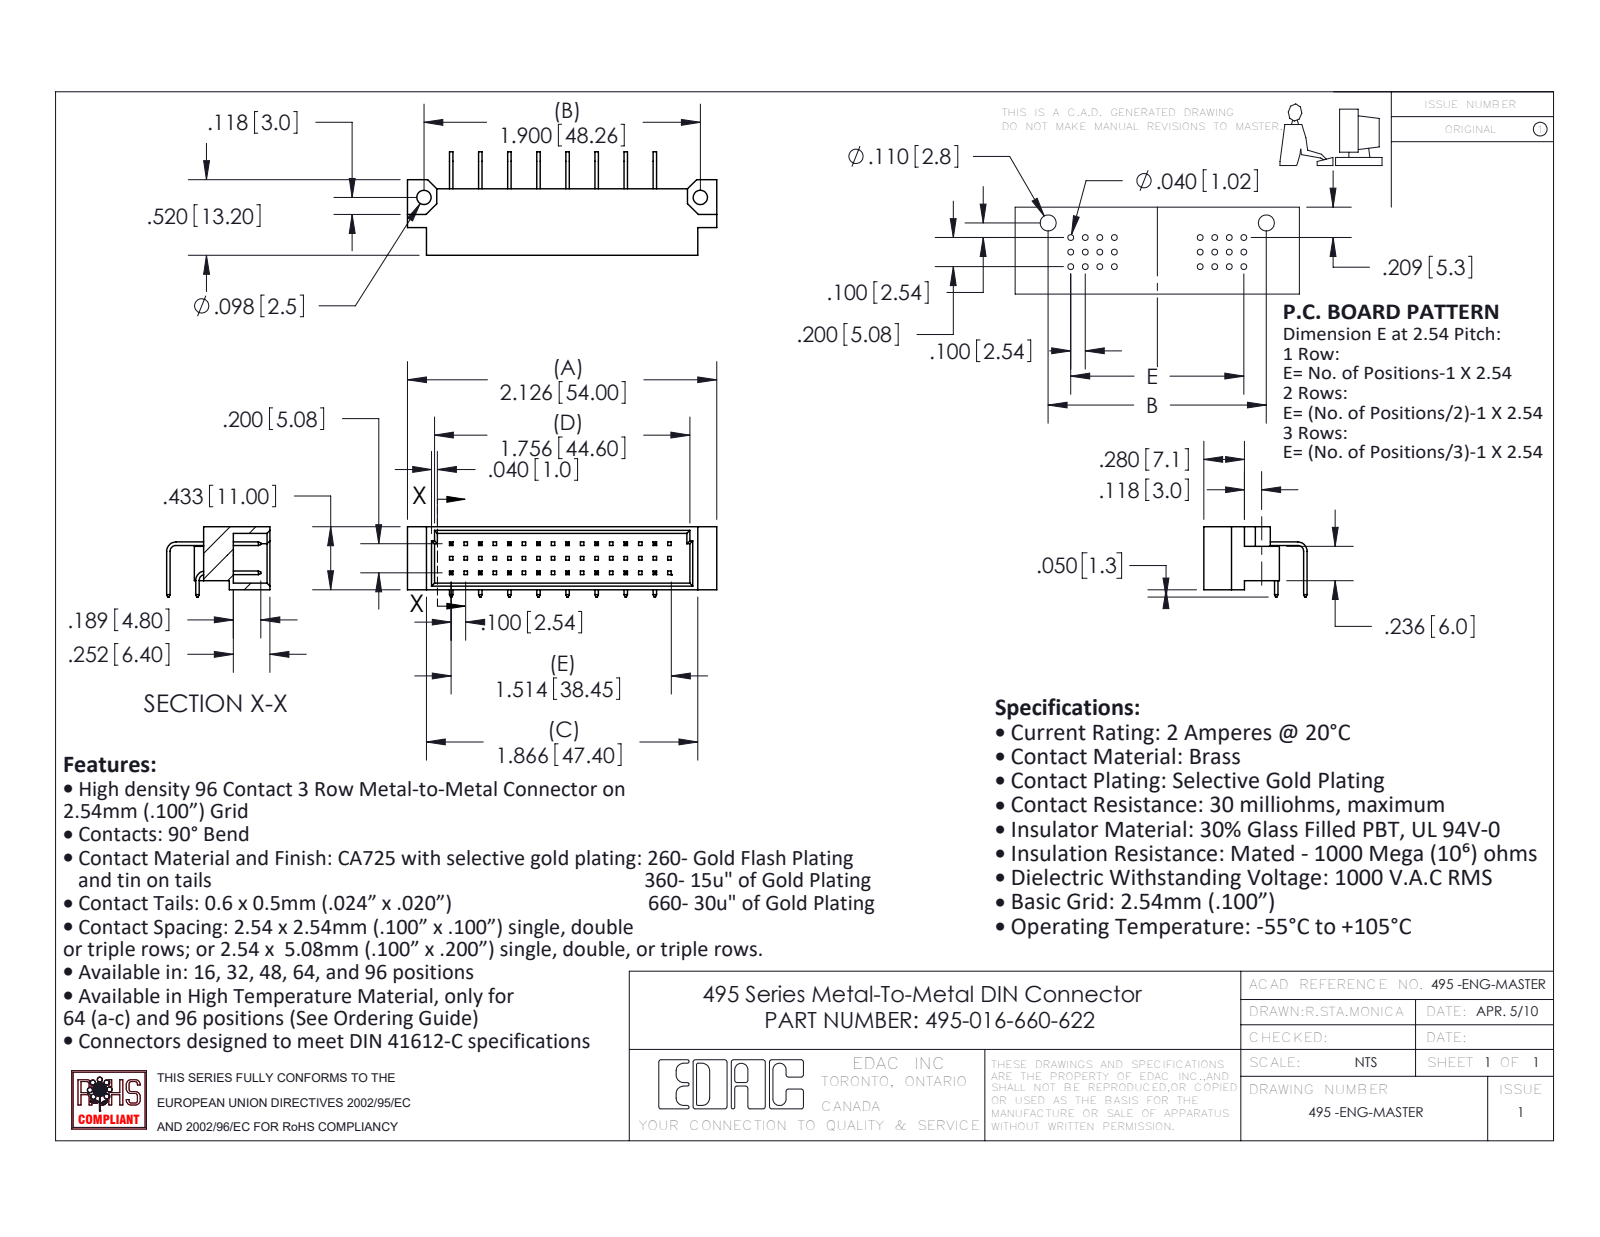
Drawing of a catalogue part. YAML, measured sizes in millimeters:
part_name: "495-290-3; 495 Part_48; 495-016-660-622; 495-290-1"
step_written_by: "SolidWorks 2020 (AUTOMOTIVE_DESIGN)"
units: millimeters
bodies: {solids: 17, faces: 530, planar: 494, cylindrical: 36, other: 0}
overall_size: [54, 18.05, 12.27]
volume: 3565
surface_area: 4729
round_holes:
  - {diameter: 2.49, count: 2}
partial_cylinders:
  - {radius: 1.02, count: 2}
  - {radius: 1.65, count: 2}
face_to_face_distances: [5.08, 1.14, 9.86, 5.2, 11, 0.61, 15.24, 1.6, 10.16, 8.72]
hole_center_spacings: [48.26]
